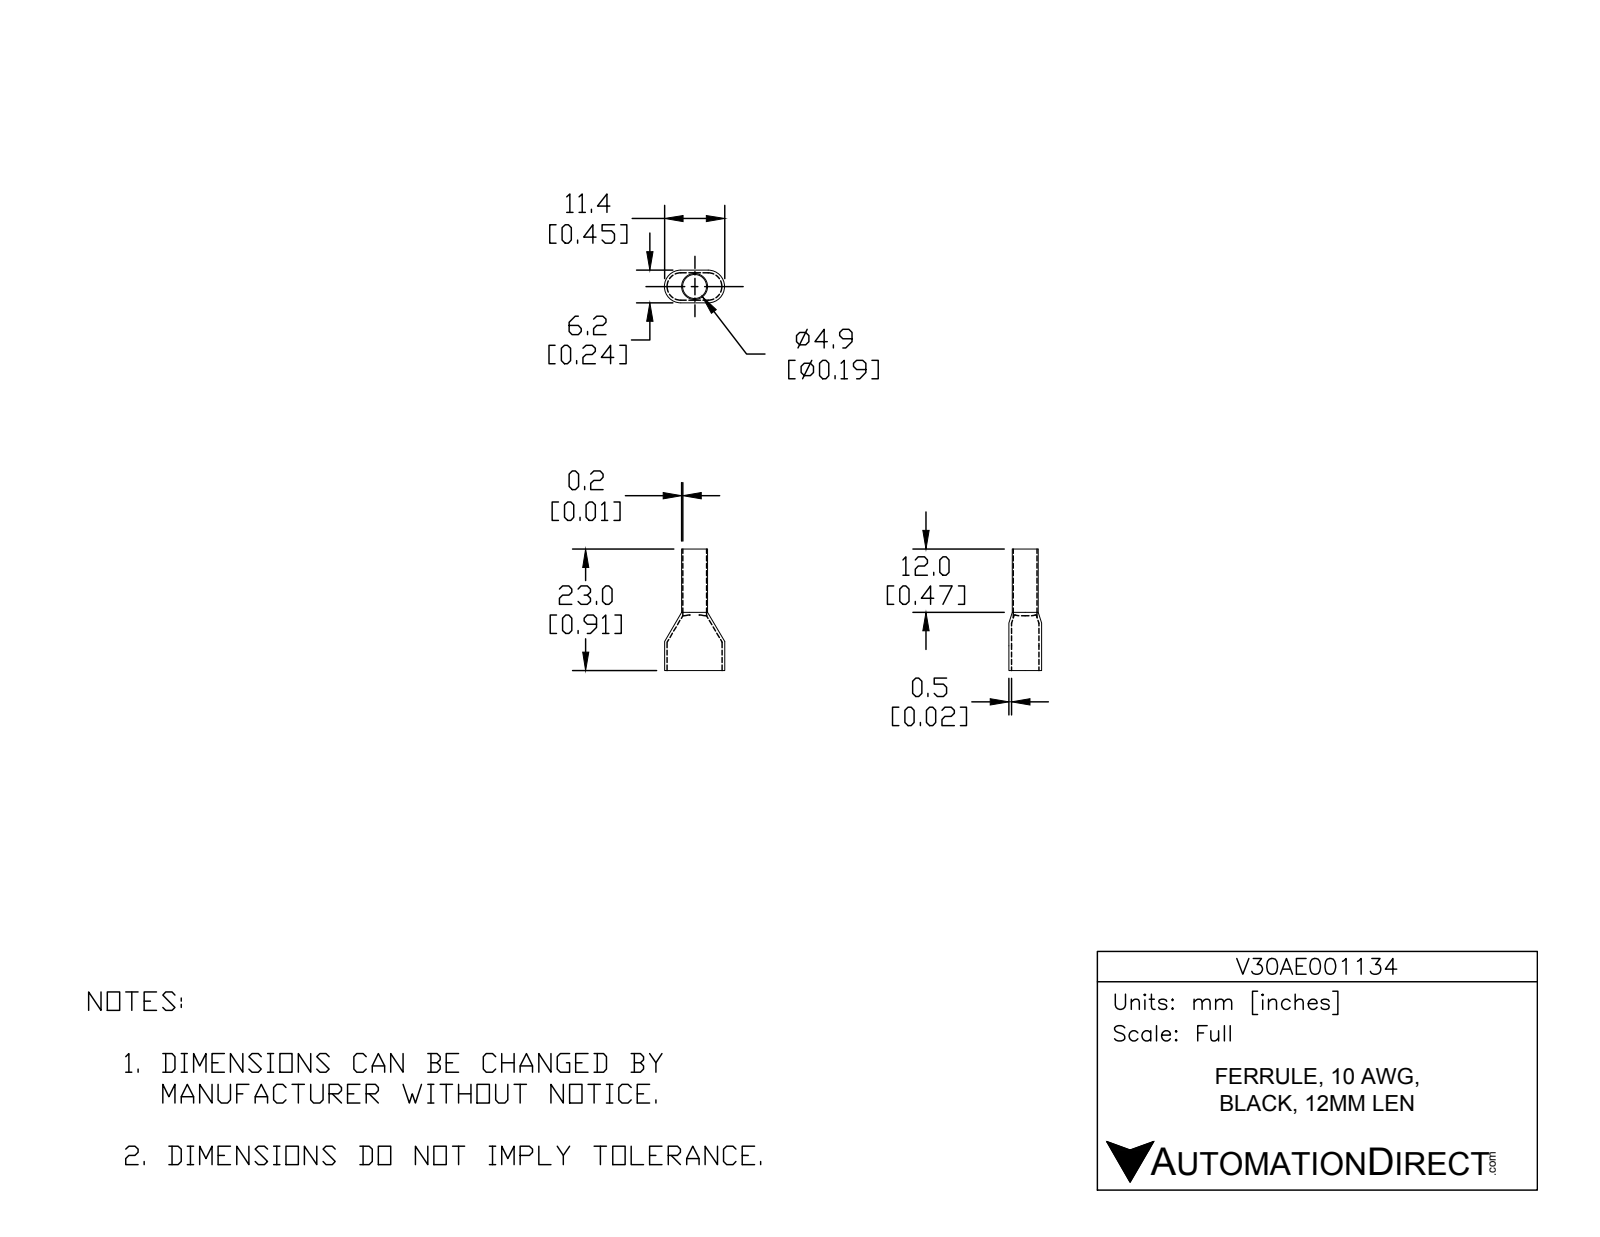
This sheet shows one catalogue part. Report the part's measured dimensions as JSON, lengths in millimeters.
{"part_name": "V30AE001139", "step_written_by": "SolidWorks 2017 (AUTOMOTIVE_DESIGN)", "units": "millimeters", "bodies": {"solids": 2, "faces": 38, "planar": 16, "cylindrical": 22, "other": 0}, "overall_size": [23, 11.4, 6.2], "volume_mm3": 174, "surface_area_mm2": 939, "round_holes": [[4.5, 1]], "round_bosses_or_shafts": [[4.9, 1]], "partial_cylinders_radius": [[2.6, 6], [3.1, 6]], "face_to_face_distances": [0.5, 5.7, 6.2, 5.2, 11, 23, 12, 10.5, 12.5]}
